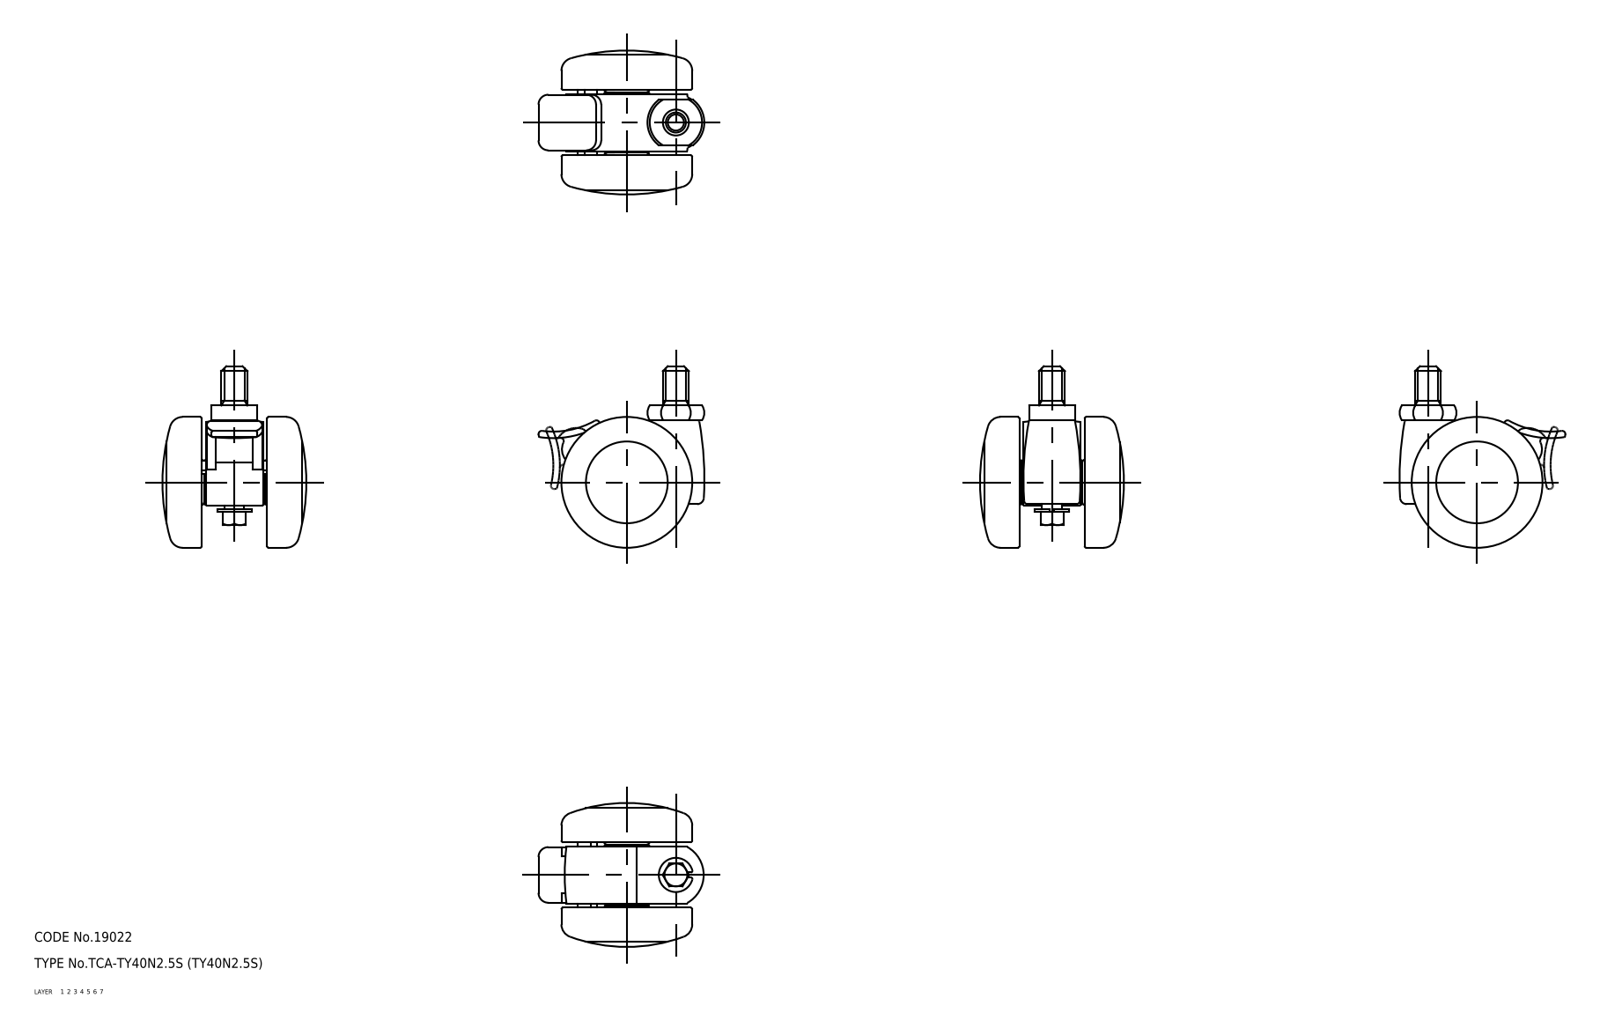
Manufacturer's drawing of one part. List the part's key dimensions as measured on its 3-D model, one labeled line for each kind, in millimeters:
Part name (STEP PRODUCT): wheel; main shaft; lever; TY40N2_5S_10352_36
STEP written by: CADfix (AUTOMOTIVE_DESIGN)
Units: millimetres
Bodies: 5 solids, 193 faces (0 planar, 0 cylindrical, 193 other)
Overall size (bounding box): 55.5 × 50.72 × 44
Volume: 39 482 mm³ · Surface area: 19 032 mm²
